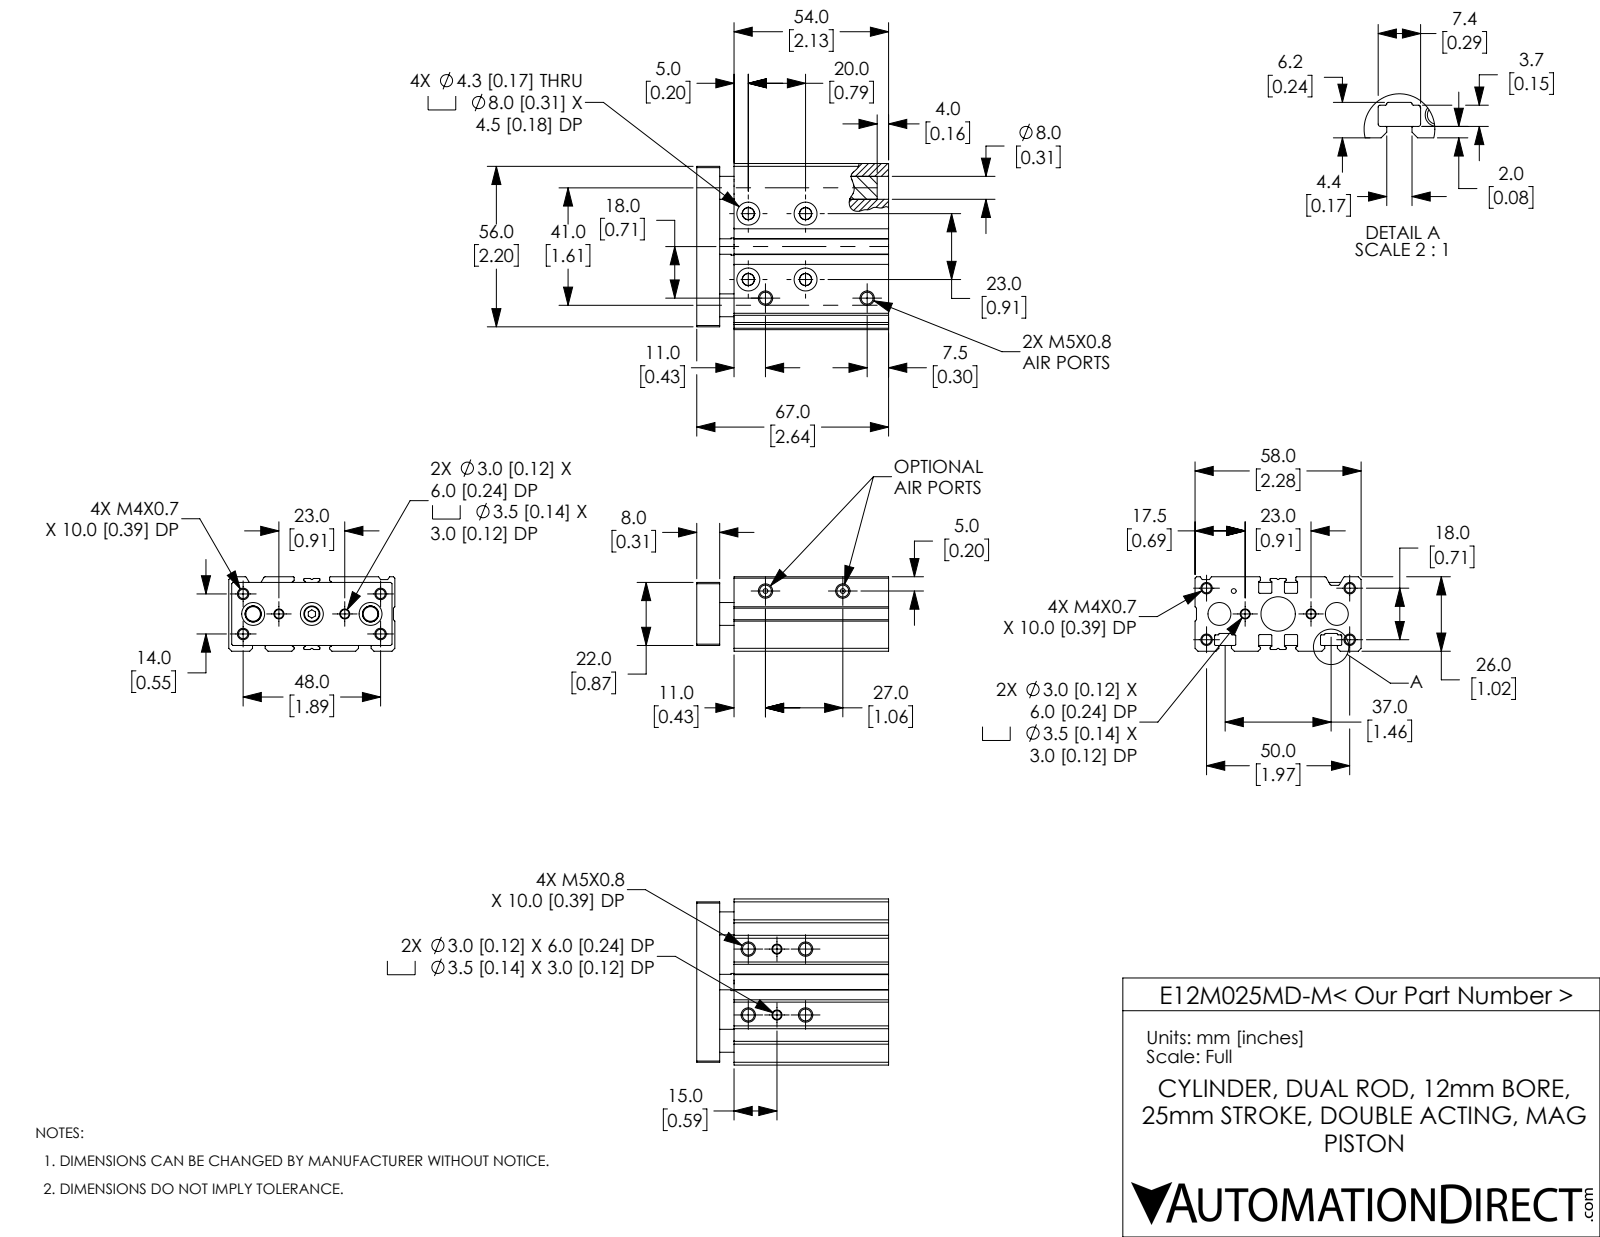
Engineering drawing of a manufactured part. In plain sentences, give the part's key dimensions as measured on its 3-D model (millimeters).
The part is named "E12M025MD-M; E12M025MD-D_BODY; E12M025MD-M_ENDPLATE". Its 3-D file was written by "SolidWorks 2019 (CONFIG_CONTROL_DESIGN)". It is 5 solids with 413 faces: 137 planar, 188 cylindrical and 88 other. Overall it measures 67 by 58 by 26 millimeters. Its volume is 74 216 cubic millimeters and its surface area 32 833 square millimeters. Round holes: 8 of diameter 3.24, 8 of diameter 4.13, 7 of diameter 8, 4 of diameter 3, 4 of diameter 3.5, 4 of diameter 4.3, 3 of diameter 1.67, 3 of diameter 4, 2 of diameter 5.59, 1 of diameter 8, 1 of diameter 12, 1 of diameter 12. Round bosses or shafts: 1 of diameter 6, 1 of diameter 5.59. Partial cylindrical surfaces (rounded edges, fillets, slot ends): 20 of radius 0.4, 18 of radius 0.2, 8 of radius 0.25, 6 of radius 0.3, 4 of radius 0.5. The main face-to-face distances are 26, 8, 2, 13, 5.8, 59, 24, 5, 54, 58. The hole center spacings are 2.24, 7.83, 10, 10.06, 14.33, 16.03, 16.22, 23.
